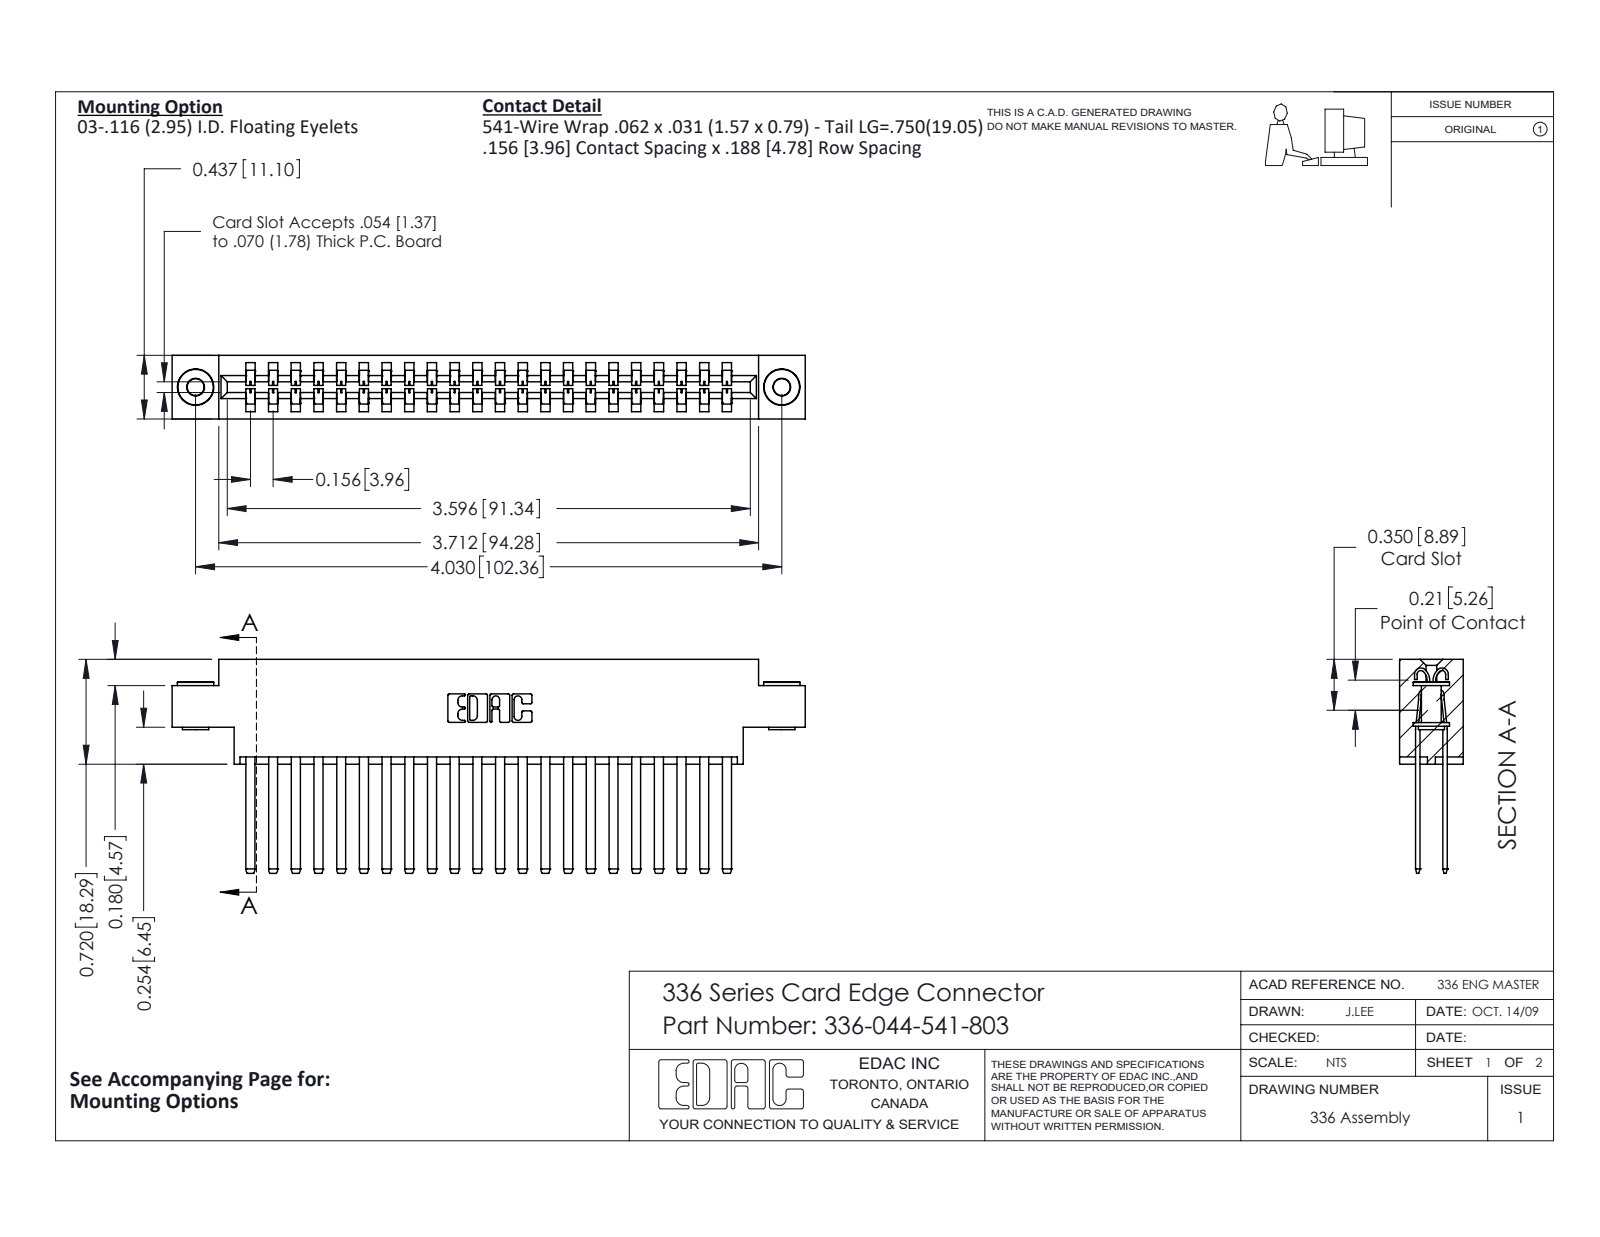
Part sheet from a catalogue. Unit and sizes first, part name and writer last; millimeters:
Units: millimetres
Overall size (bounding box): 110.6 × 37.3 × 11.1
Round holes (diameter × count): ⌀2.9 ×2, ⌀4 ×2
Round bosses / shafts (diameter × count): ⌀6.4 ×2, ⌀4.6 ×2, ⌀3.5 ×2
Partial cylindrical surfaces — rounded edges, fillets, slot ends (radius × count): R0.1 ×88, R1.4 ×44, R0.3 ×22, R0.2 ×6, R0.8 ×6, R0.6 ×4, R1 ×4, R0.7 ×3
Main face-to-face distances: 4.8, 0.8, 8.3, 3.6, 7.5, 2.8, 11.1, 0.8, 4, 4.6
Hole centre spacings: 102.4
Volume: 16 440 mm³ · Surface area: 20 920 mm²
Bodies: 47 solids, 2004 faces (1228 planar, 768 cylindrical, 8 other)
Part name (STEP PRODUCT): 345-250-002_345-250-002-102; 336-290-001_336-290-541; 336-044-541-803; 336 Part_Offset - .156 Dia - TH
STEP written by: SolidWorks 2020 (CONFIG_CONTROL_DESIGN)
